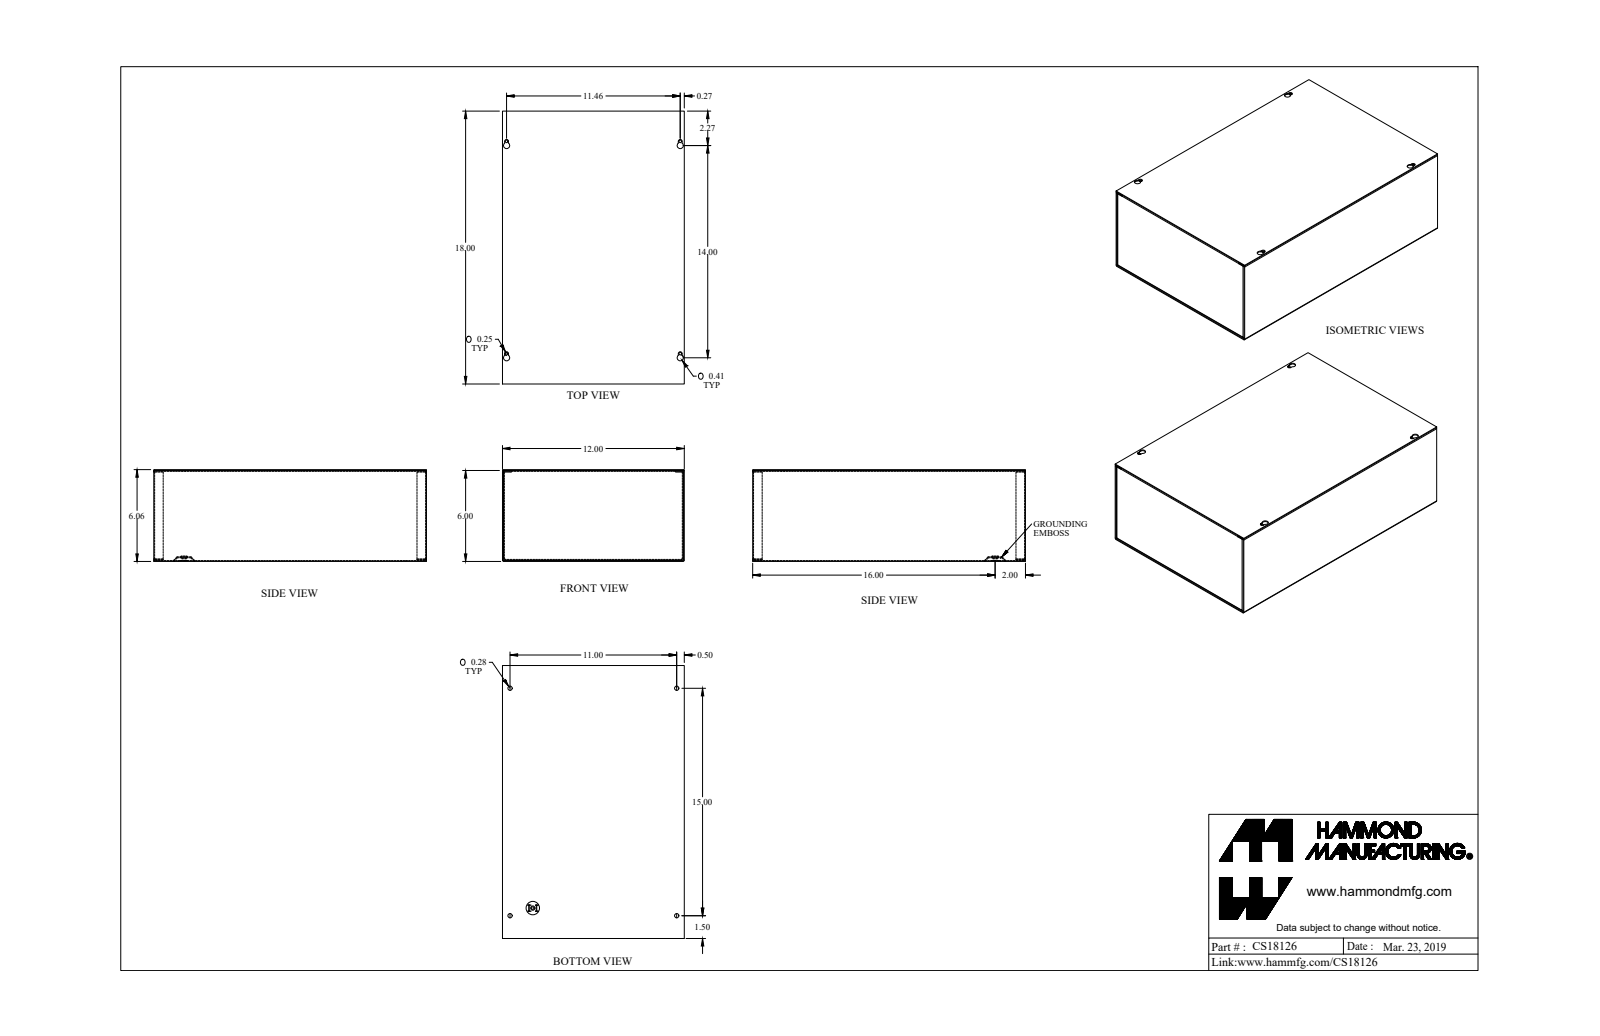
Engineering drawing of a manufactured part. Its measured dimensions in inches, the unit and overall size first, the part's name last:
Units: inches
Overall size (bounding box): 18 × 12 × 6.057
Round holes (diameter × count): ⌀0.17 ×5, ⌀0.281 ×4, ⌀0.5 ×1
Round bosses / shafts (diameter × count): ⌀0.492 ×1, ⌀0.284 ×1
Partial cylindrical surfaces — rounded edges, fillets, slot ends (radius × count): R0.029 ×12, R0.086 ×12, R0.057 ×8, R0.125 ×4, R0.203 ×4
Main face-to-face distances: 0.057, 6, 5.943, 6.057, 11.943, 17.943, 12, 11.886, 18, 17.886
Hole centre spacings: 0.55, 11.241, 14.502, 18.34, 11, 11.46, 14, 15
Volume: 47.54 in³ · Surface area: 1 682 in²
Bodies: 4 solids, 205 faces (125 planar, 72 cylindrical, 8 other)
Part name (STEP PRODUCT): CS18126_Default
STEP written by: SolidWorks 2019 (CONFIG_CONTROL_DESIGN)
